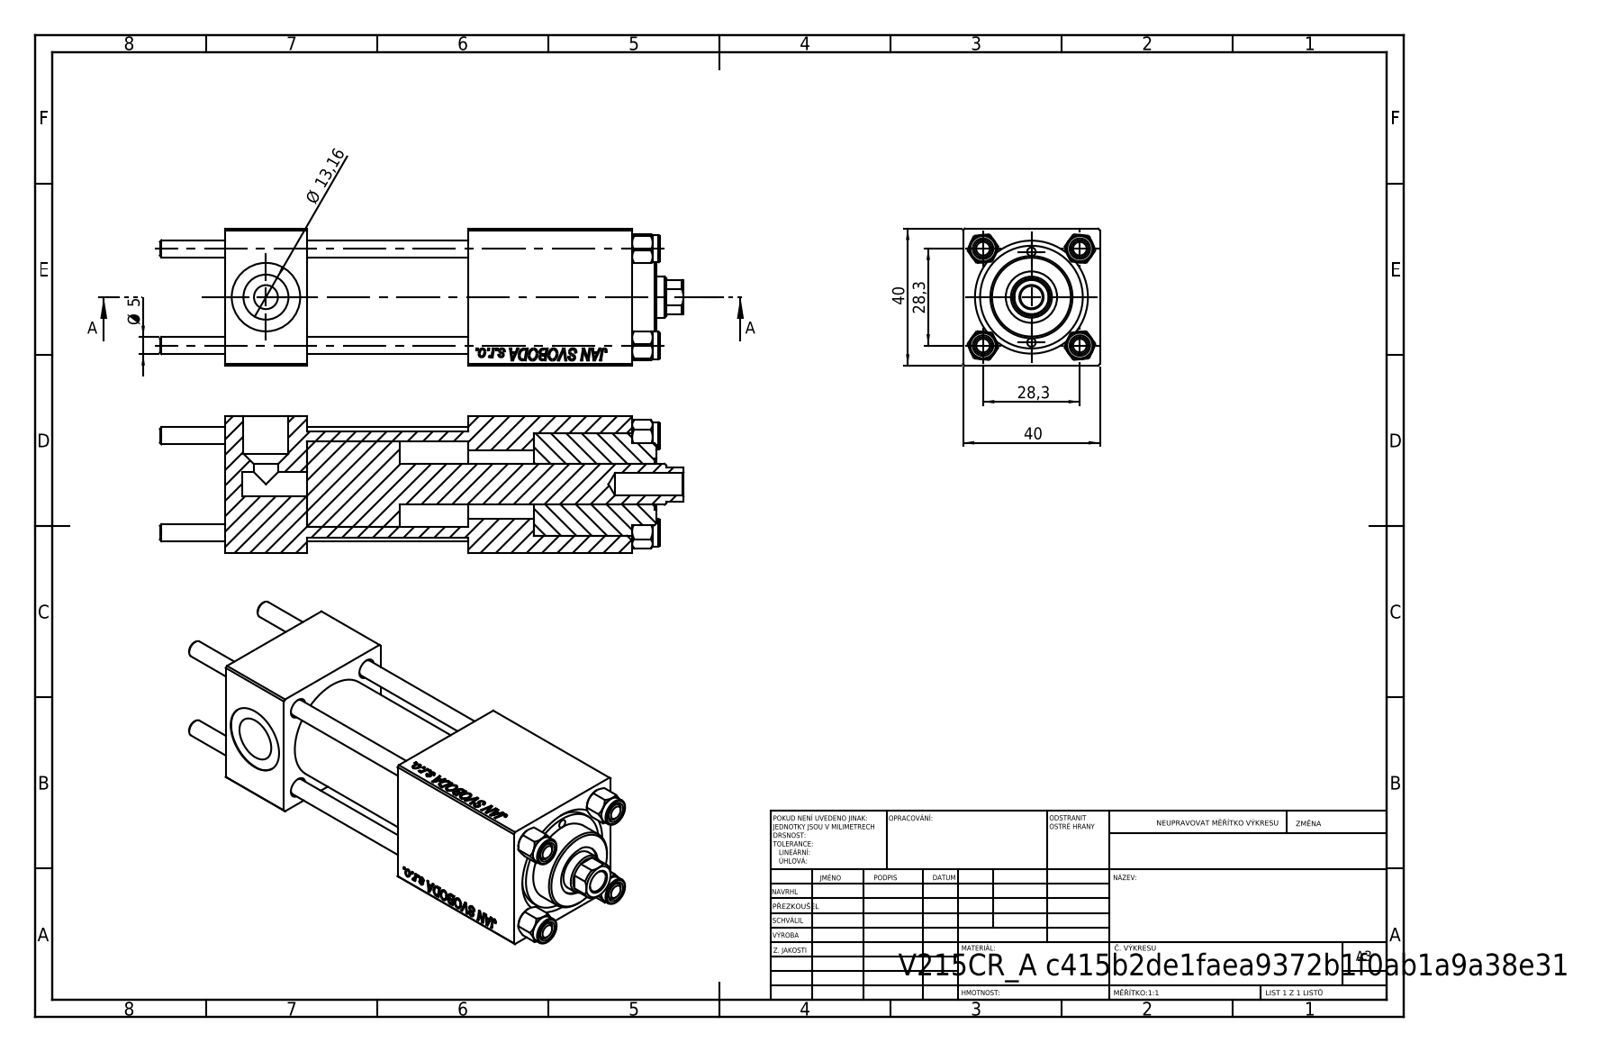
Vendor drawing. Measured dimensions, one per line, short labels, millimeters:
name: V215CR_BODY_A; V215_VC_A; V215CR_VCP; CR025_012_A_0_G_A_G_M_020_+#_##_TYCINKA (+1 more)
written by: SolidWorks 2019 (CONFIG_CONTROL_DESIGN)
unit: mm
bodies: 11 solids, 1138 faces (519 planar, 83 cylindrical, 536 other)
size: 153 × 40 × 40
volume: 144 694 mm³; area: 58 951 mm²
holes: 4× ⌀5, 3× ⌀20, 2× ⌀2.5, 2× ⌀7, 2× ⌀13.16, 1× ⌀6.5, 1× ⌀12, 1× ⌀15, 1× ⌀25, 1× ⌀30
bosses: 4× ⌀8, 1× ⌀31, 1× ⌀24
rounds: 1× R5.5
face distances: 40, 24, 90.3, 66.3, 119, 95, 28.7, 71, 47, 19.3
hole spacings: 14.18, 20.01, 28.3, 30.84, 13.25, 40.02, 26.5
